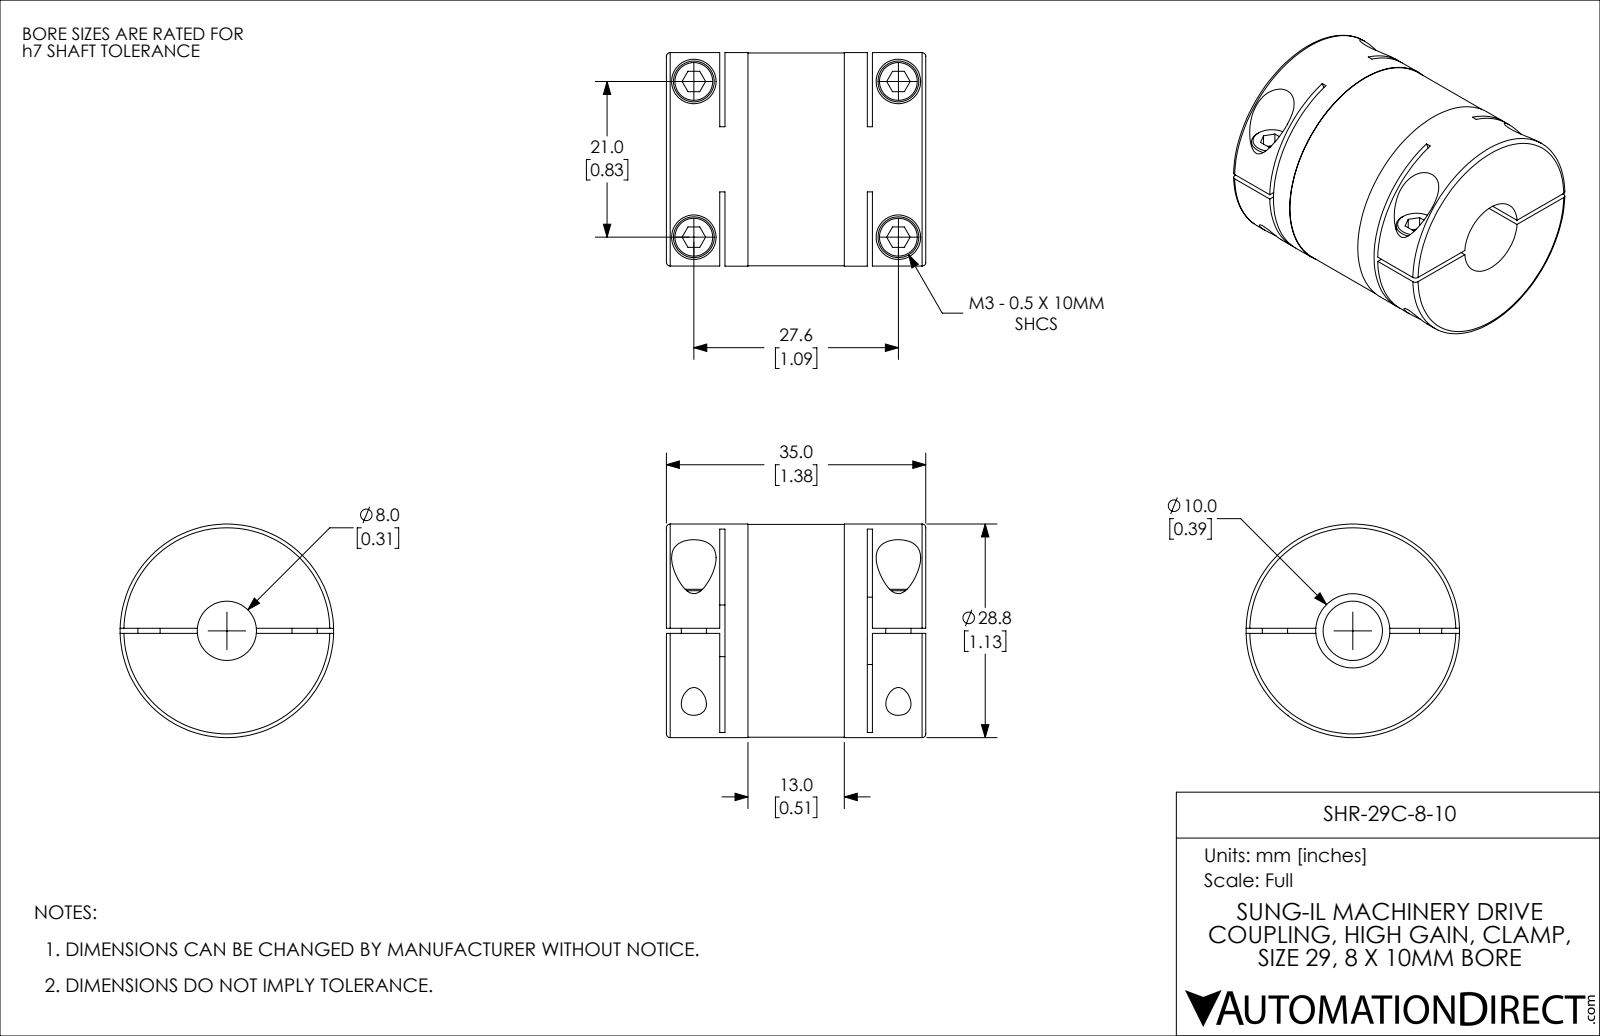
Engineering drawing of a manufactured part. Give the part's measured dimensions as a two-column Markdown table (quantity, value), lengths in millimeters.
| quantity | value |
| --- | --- |
| part name | SHR-29C-8-10 |
| STEP written by | SolidWorks 2021 (CONFIG_CONTROL_DESIGN) |
| units | millimeters |
| bodies | 1 solid, 145 faces (70 planar, 57 cylindrical, 18 other) |
| overall size | 35 × 28.8 × 28.8 |
| volume | 18 345 mm³ |
| surface area | 8 886 mm² |
| round holes (diameter × count) | 3.4 × 4, 6 × 4, 8 × 1, 10 × 1, 12 × 1 |
| round bosses / shafts (diameter × count) | 5.5 × 4, 3 × 2, 28.8 × 1, 28.7 × 1 |
| partial cylindrical surfaces (radius × count) | 37.5 × 2 |
| main face-to-face distances | 0.7, 7.9, 27.1, 7.2, 27.8, 19.9, 35, 19.2, 20.6, 11 |
| hole center spacings | 21, 27.6, 34.68 |
